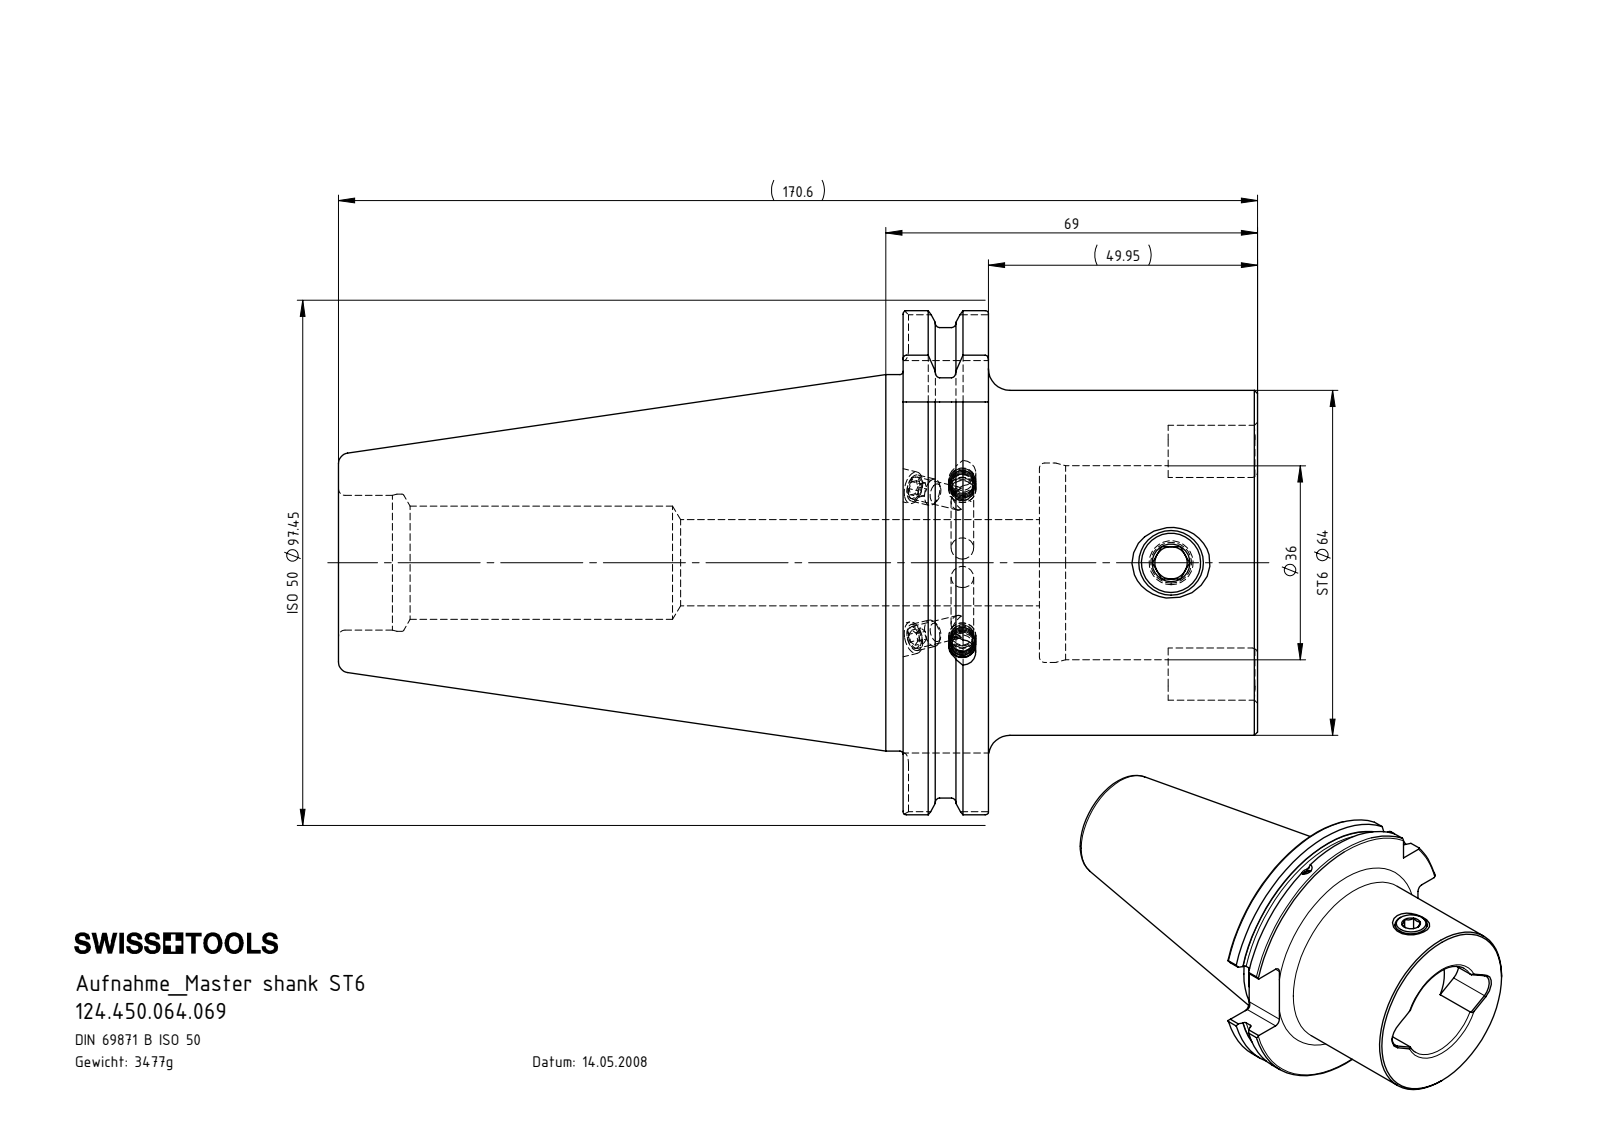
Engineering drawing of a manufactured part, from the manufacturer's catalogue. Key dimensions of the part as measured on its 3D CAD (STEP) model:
Part name (STEP PRODUCT): KVT_MB_600_050; ISO 4026 - M5 x 5_PreviewCfg; SB5-ST6.K01.069_C_mit Bundkhlung; ST6-ER1.001.018_A (+1 more)
STEP written by: SolidWorks 2017 (AUTOMOTIVE_DESIGN)
Units: millimetres
Bodies: 8 solids, 206 faces (78 planar, 46 cylindrical, 82 other)
Overall size (bounding box): 170.6 × 97.45 × 93.51
Volume: 442 969 mm³ · Surface area: 60 322 mm²
Round holes (diameter × count): ⌀4.2 ×3, ⌀6 ×3, ⌀4 ×2, ⌀5 ×1, ⌀11 ×1, ⌀16 ×1, ⌀21 ×1, ⌀25 ×1, ⌀25.45 ×1, ⌀36 ×1, ⌀37 ×1
Round bosses / shafts (diameter × count): ⌀5 ×3, ⌀91 ×1, ⌀69.85 ×1, ⌀64 ×1, ⌀12 ×1
Partial cylindrical surfaces — rounded edges, fillets, slot ends (radius × count): R2 ×8, R5.2 ×2, R48.73 ×1
Main face-to-face distances: 15.85, 65.8, 49.95, 40.5, 25.3, 9.45, 104.8, 120.65, 130.1, 170.6
